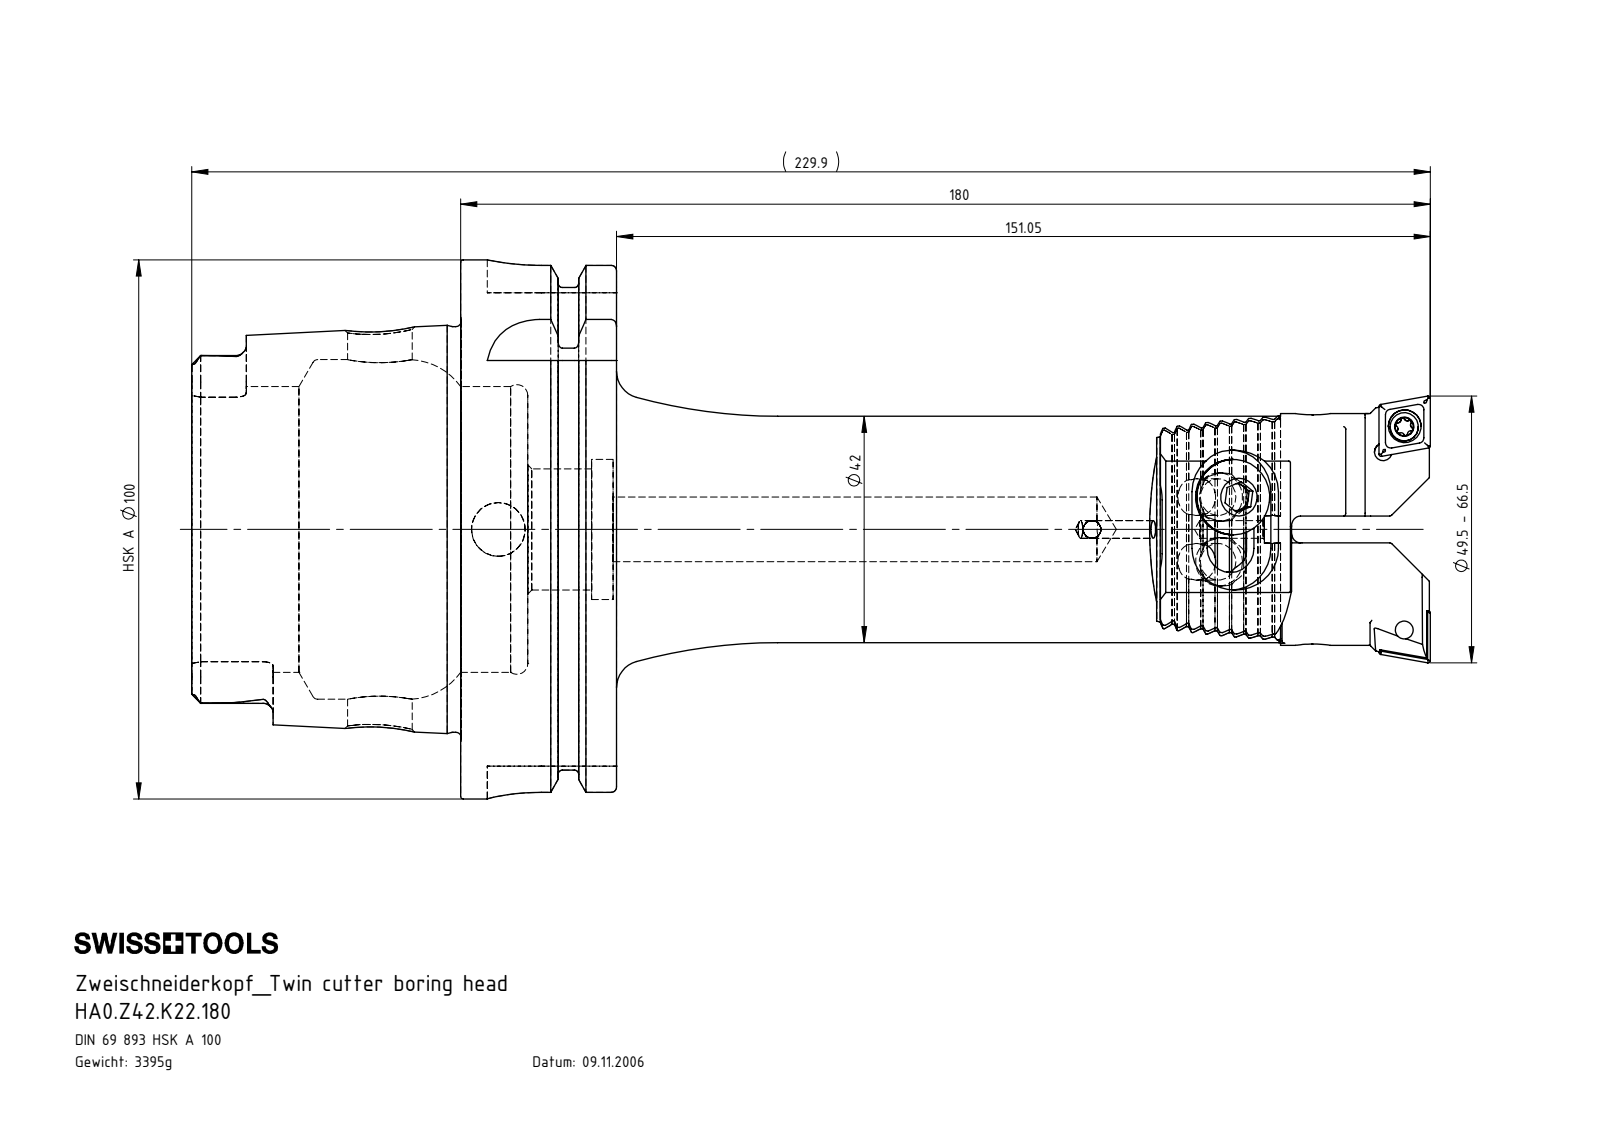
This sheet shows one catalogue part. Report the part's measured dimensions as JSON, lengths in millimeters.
{"part_name": "Z42-ER1.003.020_A_gespannt; CCMT09T304; HA0.Z42.K22.180; Z42-ER1.001.020 (+6 more)", "step_written_by": "SolidWorks 2022 (CONFIG_CONTROL_DESIGN)", "units": "millimeters", "bodies": {"solids": 13, "faces": 1032, "planar": 503, "cylindrical": 248, "other": 281}, "overall_size": [229.9, 100, 100], "volume_mm3": 432530, "surface_area_mm2": 86018, "round_holes": [[3.3, 8], [1.6, 2], [4.4, 2], [6.1, 2], [6.8, 2], [8.4, 2], [9, 2], [12, 2], [5, 1], [10, 1], [22.5, 1], [26, 1]], "round_bosses_or_shafts": [[4, 3], [14, 2], [8, 2], [5.25, 2], [100, 1], [91.95, 1], [75.26, 1], [42, 1]], "partial_cylinders_radius": [[0.2, 18], [0.2, 16], [0.34, 12], [0.59, 12], [1.9, 6], [2, 4], [4.5, 4], [4.88, 4]], "face_to_face_distances": [28.95, 2.38, 12.45, 16.5, 4.76, 11.91, 9.53, 2.42, 14.29, 2.34], "hole_center_spacings": [6.07, 6.19, 12, 34.15, 34.25, 38.67, 176.69, 23.18]}
